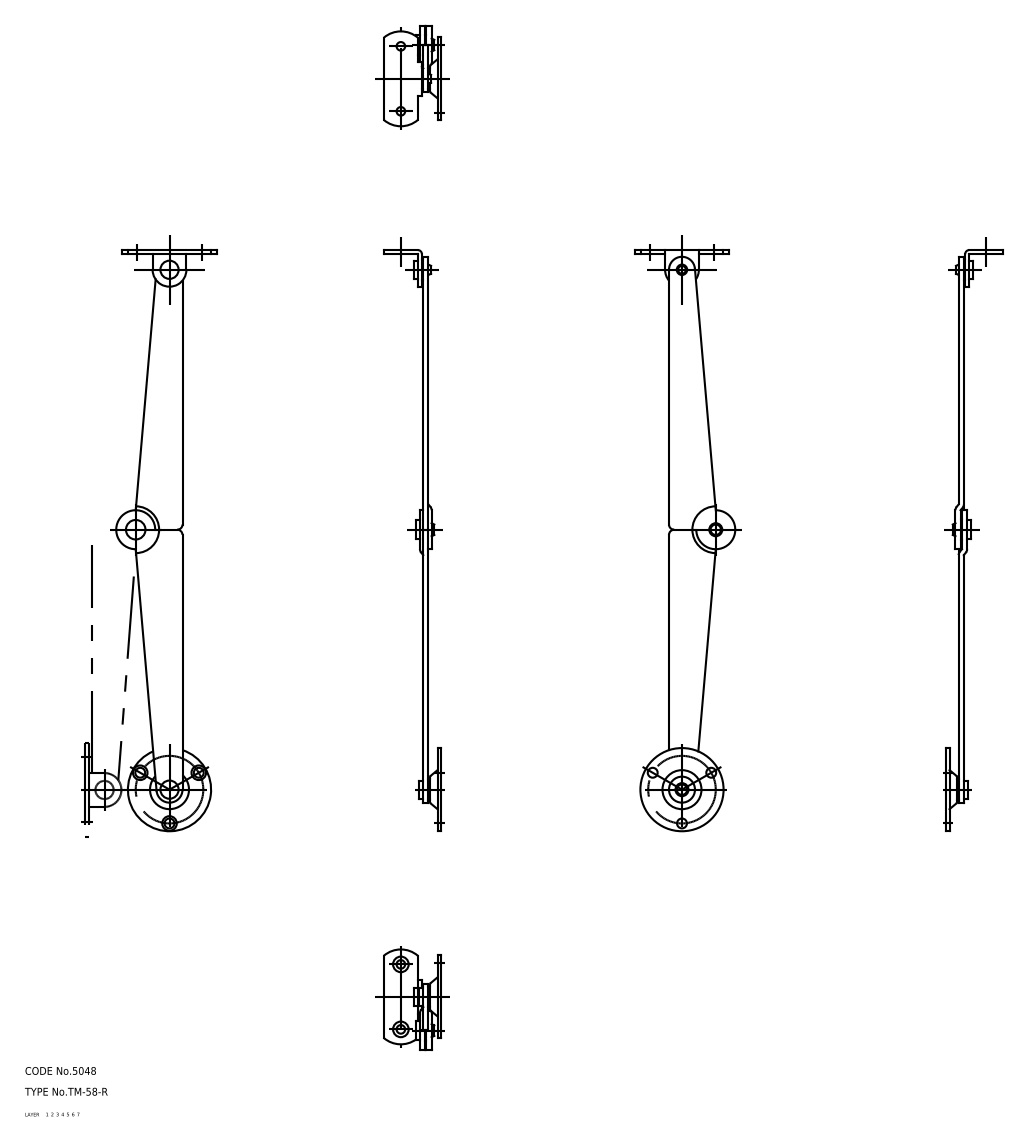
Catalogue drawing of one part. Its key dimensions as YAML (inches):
part_name: "67116218; 67116231; 67116244; 67116257 (+1 more)"
step_written_by: "CADfix (AUTOMOTIVE_DESIGN)"
units: inches
bodies: {solids: 5, faces: 117, planar: 0, cylindrical: 0, other: 117}
overall_size: [8.803, 1.526, 0.858]
volume: 0.523
surface_area: 17.2
